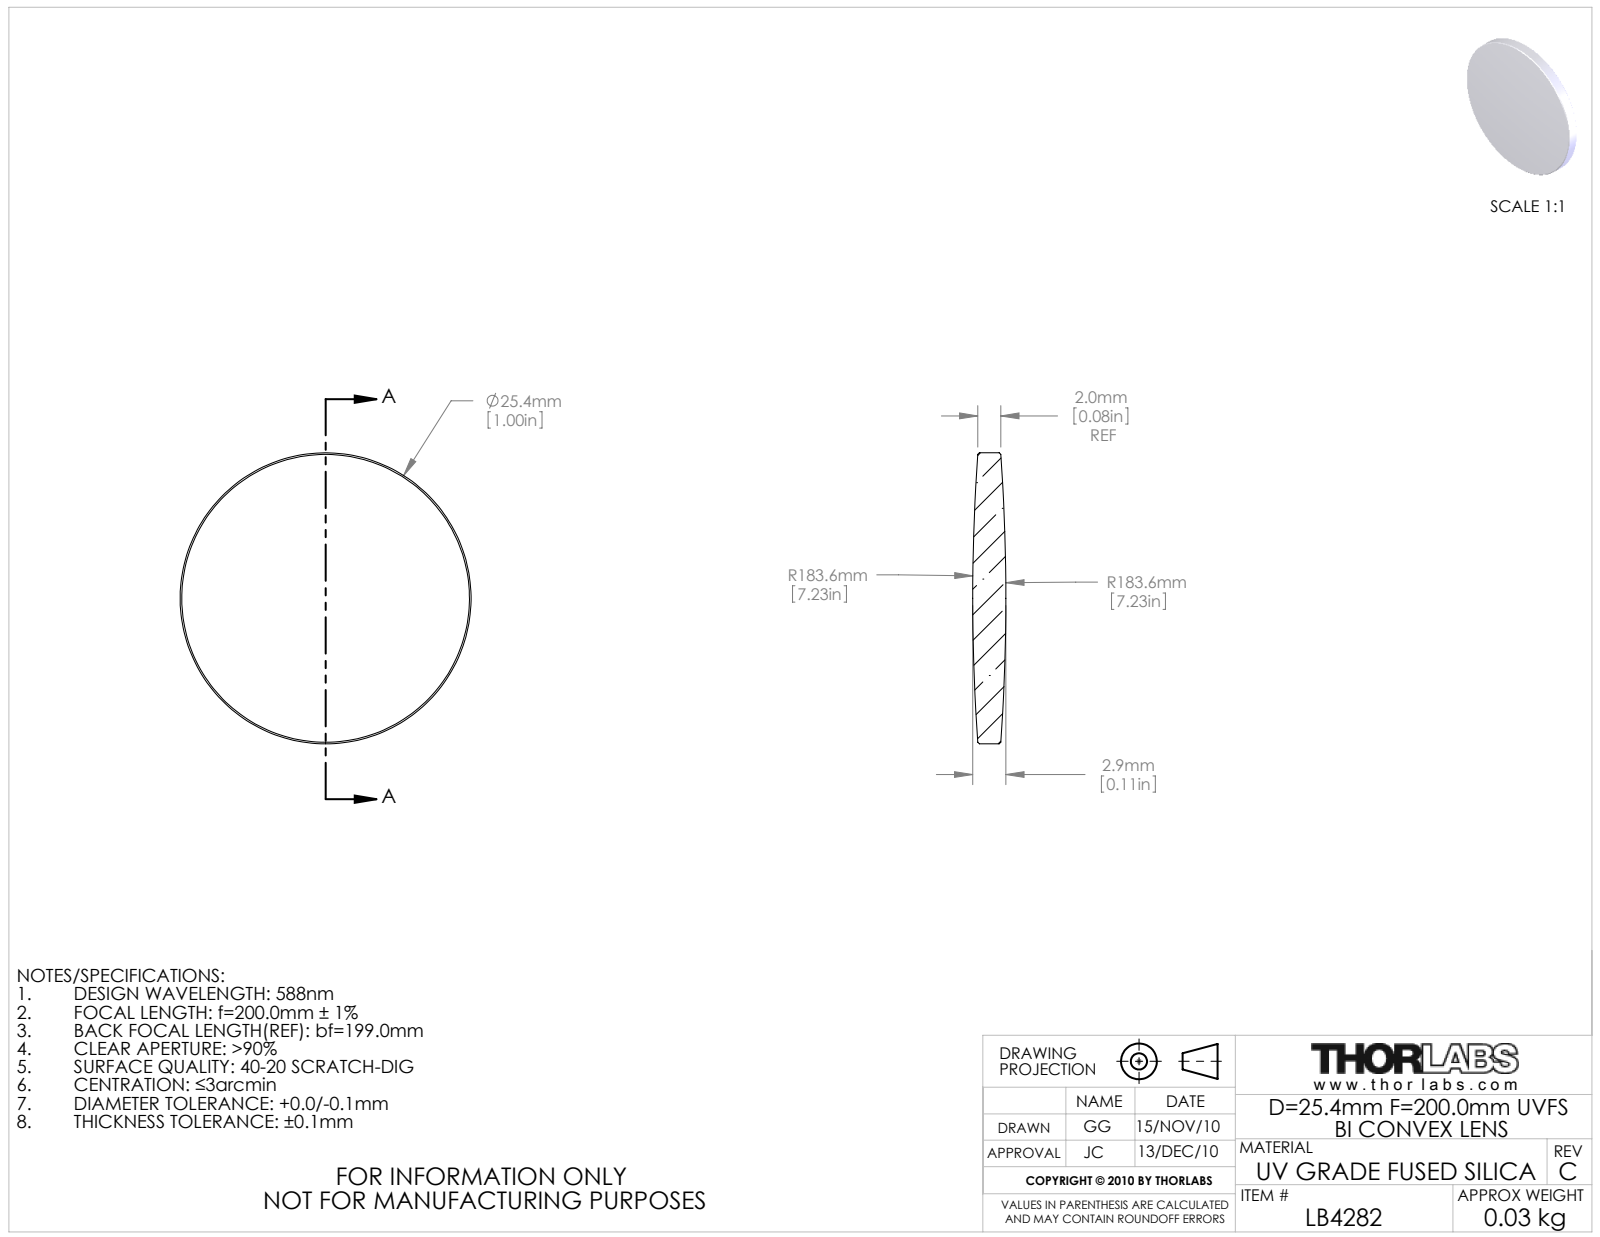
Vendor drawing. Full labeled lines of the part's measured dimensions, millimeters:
Part name (STEP PRODUCT): 3407-E0W
STEP written by: SolidWorks 2009 (AUTOMOTIVE_DESIGN)
Units: millimetres
Bodies: 1 solid, 10 faces (0 planar, 2 cylindrical, 8 other)
Overall size (bounding box): 25.4 × 25.4 × 2.9
Volume: 1 233 mm³ · Surface area: 1 161 mm²
Round bosses / shafts (diameter × count): ⌀25.4 ×1
